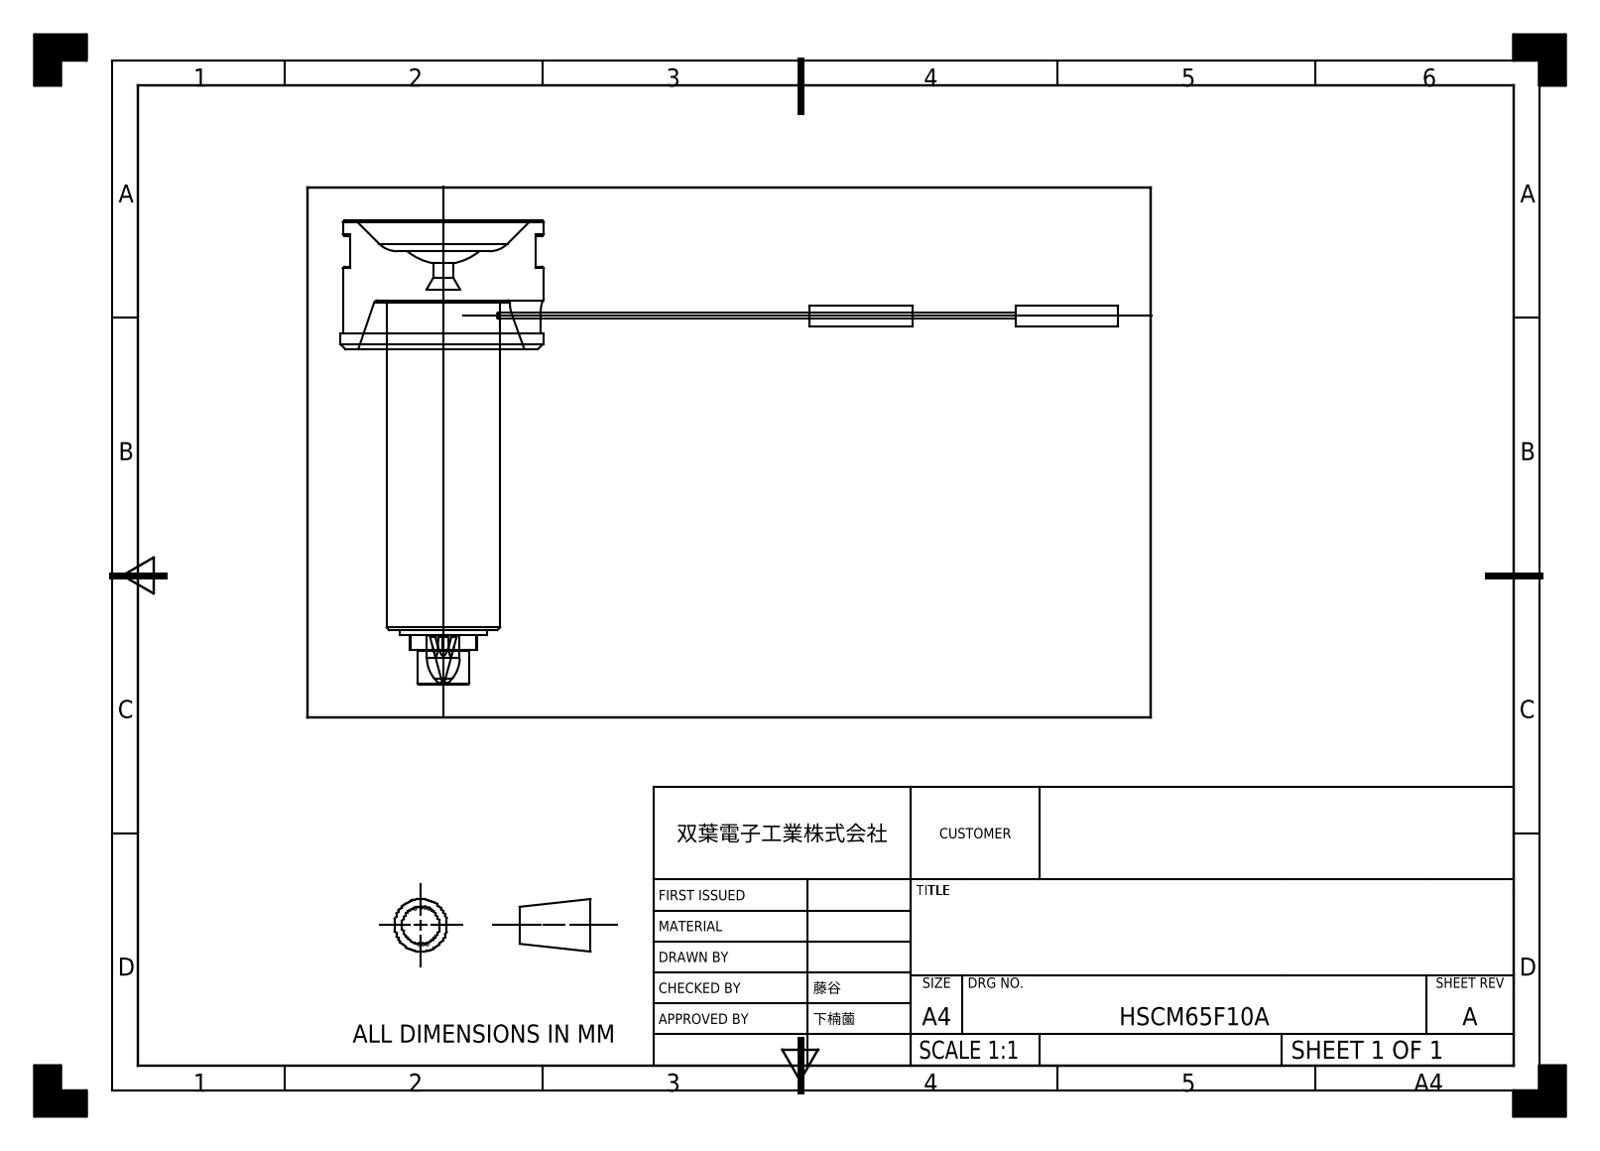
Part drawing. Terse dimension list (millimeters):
name: HSCM65F10A
written by: SIEMENS PLM Software NX 2023 (AUTOMOTIVE_DESIGN)
unit: mm
bodies: 1 solid, 74 faces (30 planar, 23 cylindrical, 21 other)
size: 151 × 90 × 40
volume: 44 724 mm³; area: 12 605 mm²
holes: 1× ⌀2, 1× ⌀4, 1× ⌀6.35
bosses: 2× ⌀4, 2× ⌀1.2, 1× ⌀40, 1× ⌀39, 1× ⌀22, 1× ⌀16.9, 1× ⌀10
rounds: 3× R2.8, 2× R3, 1× R7.45
face distances: 9.5, 25, 74.5, 65, 15.5, 79.5, 64, 54.5, 3, 6
